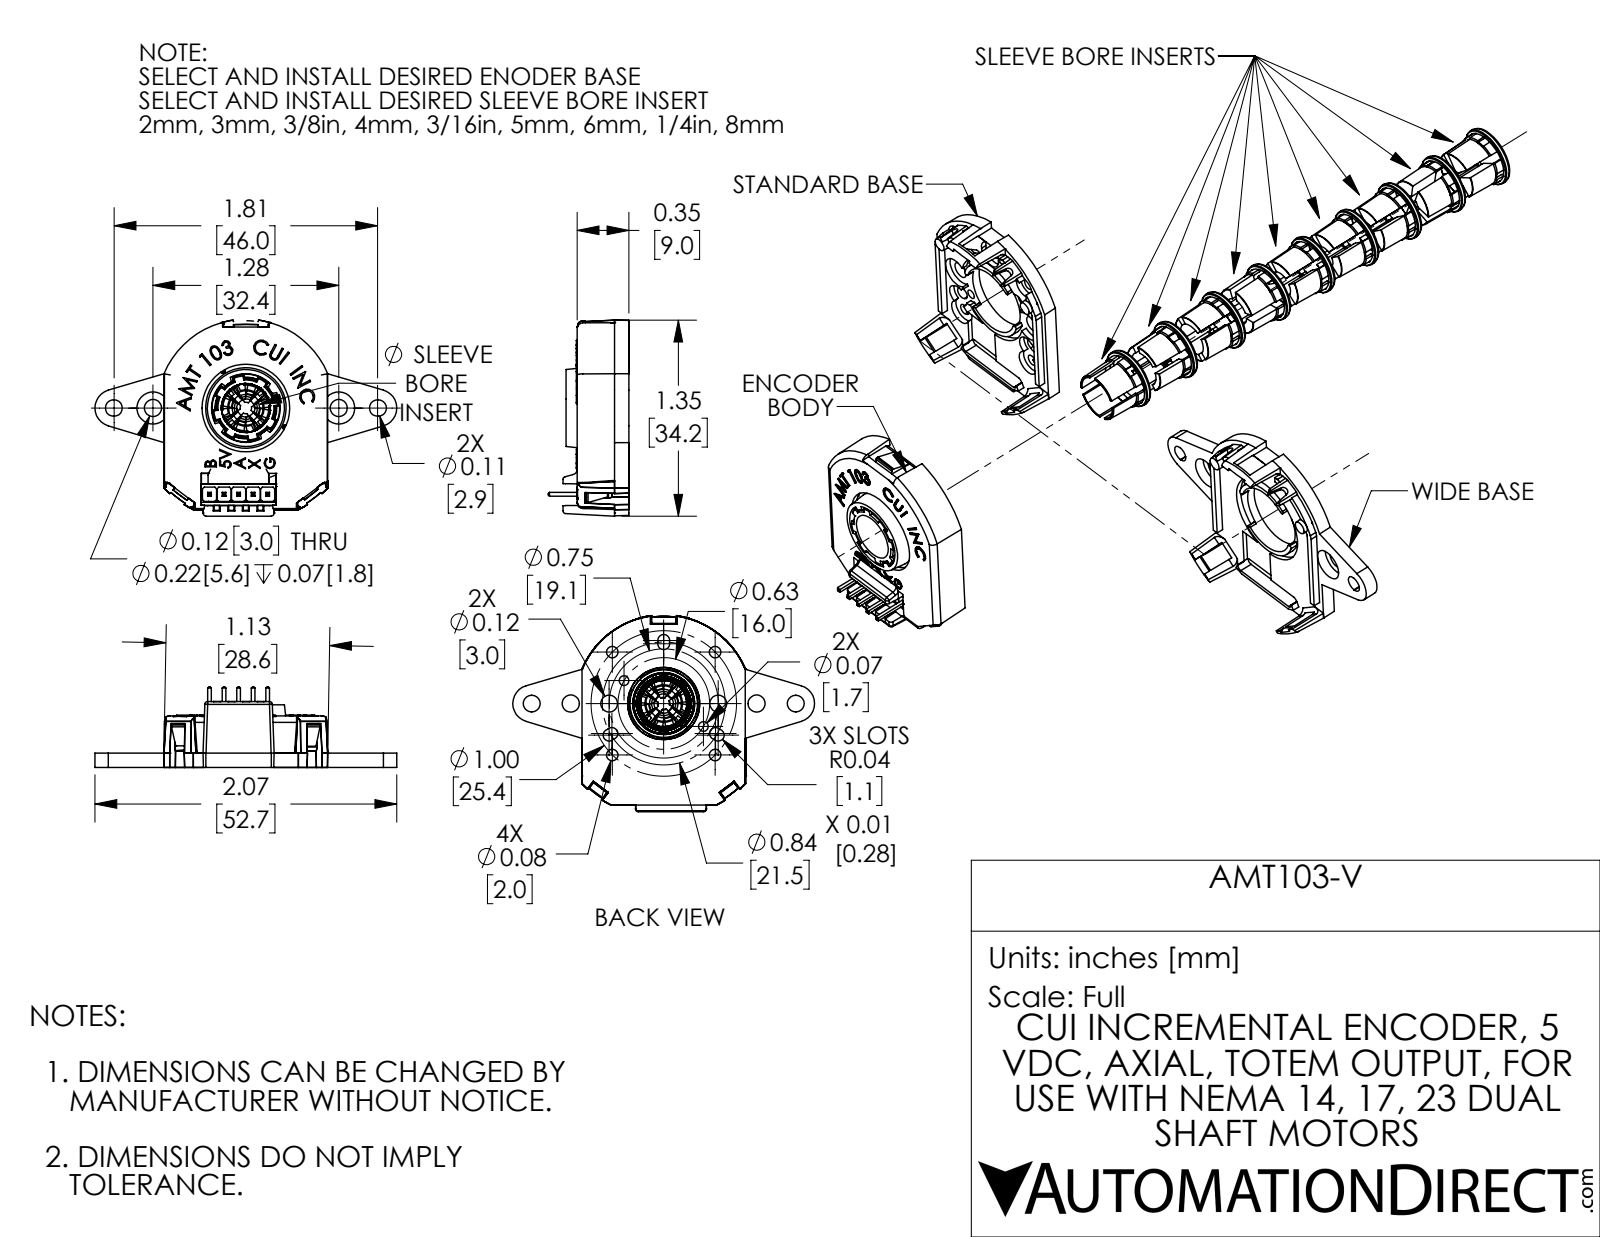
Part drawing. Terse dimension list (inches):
name: CUI_cui_amt103s from 112s-0048-2000-w 4b r1
written by: SolidWorks 2017 (AUTOMOTIVE_DESIGN)
unit: in
bodies: 32 solids, 5437 faces (4139 planar, 483 cylindrical, 815 other)
size: 5.764 × 4.573 × 1.347
volume: 0.507 in³; area: 25.24 in²
holes: 5× ⌀0.066, 5× ⌀0.079, 2× ⌀0.031, 2× ⌀0.061, 2× ⌀0.067, 2× ⌀0.116, 2× ⌀0.118, 2× ⌀0.161, 2× ⌀0.177, 2× ⌀0.22, 2× ⌀0.496, 1× ⌀0.057
bosses: 4× ⌀0.059, 2× ⌀0.098, 1× ⌀0.465, 1× ⌀0.413, 1× ⌀0.356, 1× ⌀0.078
rounds: 41× R0.039, 12× R0.02, 11× R0.079, 8× R0.016, 6× R0.041, 4× R0.028, 4× R0.03, 4× R0.056
face distances: 0.085, 0.098, 0.039, 0.183, 2.058, 1.973, 1.875, 0.03, 2.02, 1.981
hole spacings: 0.1, 0.5, 0.2, 0.354, 0.707, 0.3, 0.188, 0.212
